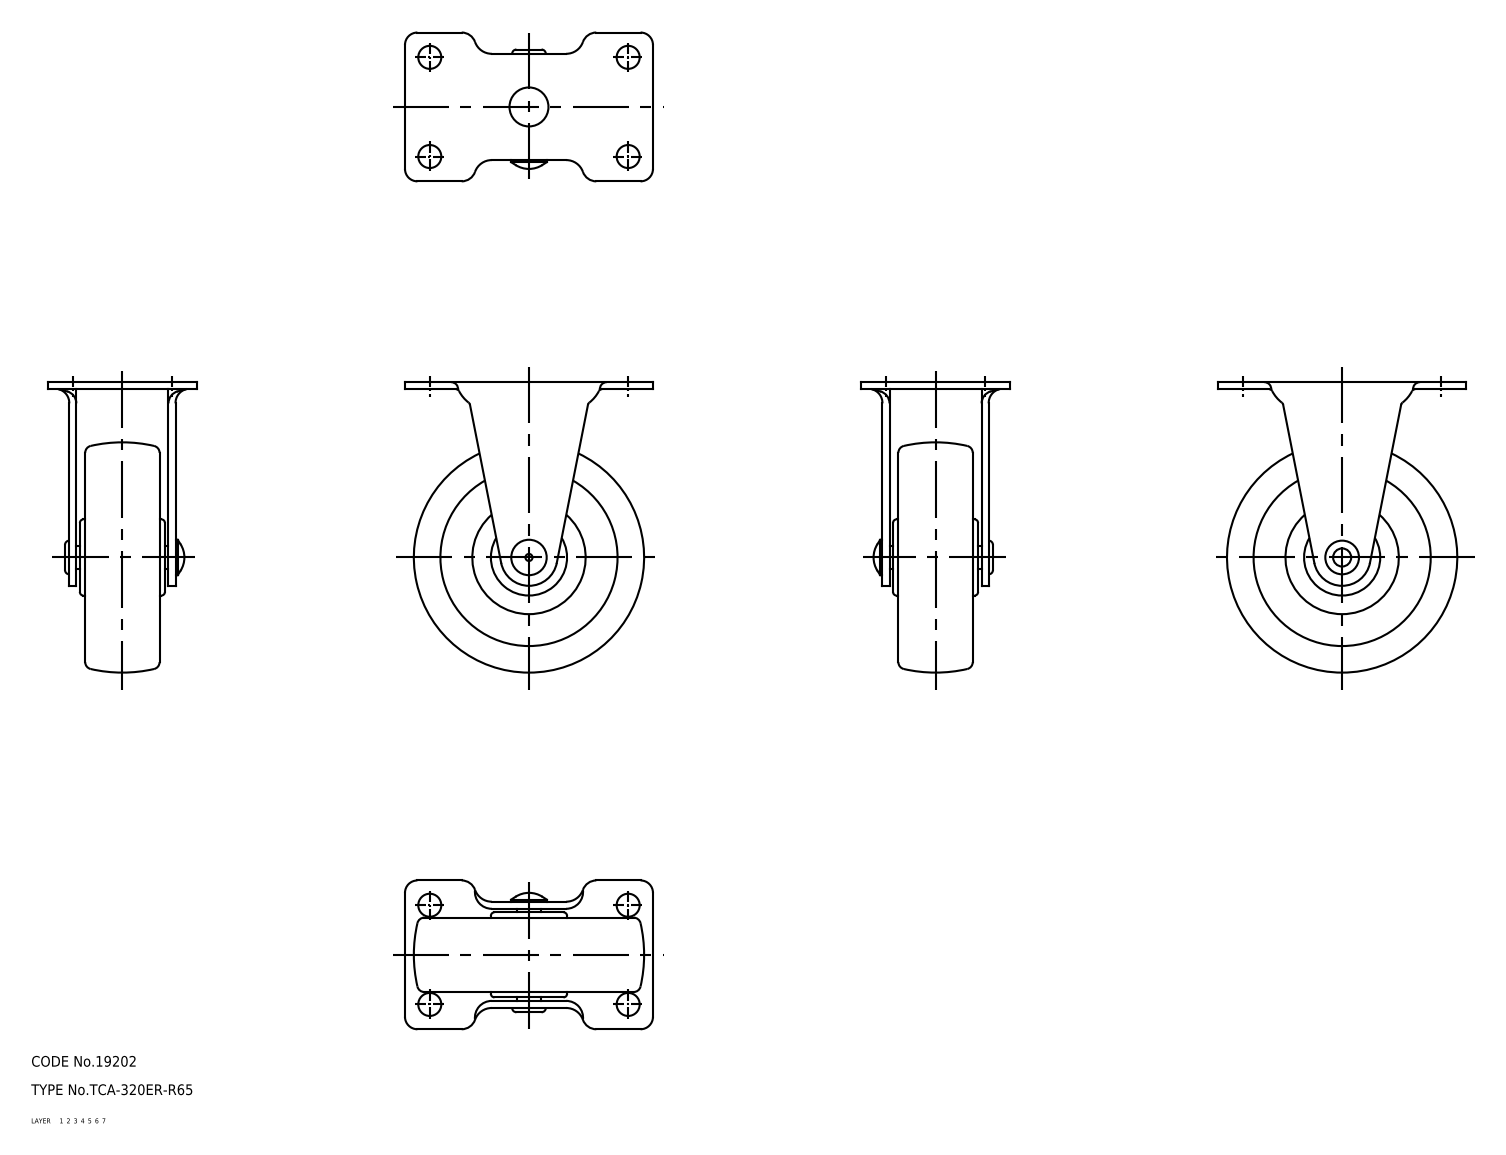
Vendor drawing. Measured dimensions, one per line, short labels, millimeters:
name: wheel; axle; 320ER_R65_5295_36
written by: CADfix (AUTOMOTIVE_DESIGN)
unit: mm
bodies: 3 solids, 139 faces (0 planar, 0 cylindrical, 139 other)
size: 82 × 70 × 42
volume: 74 398 mm³; area: 23 144 mm²
